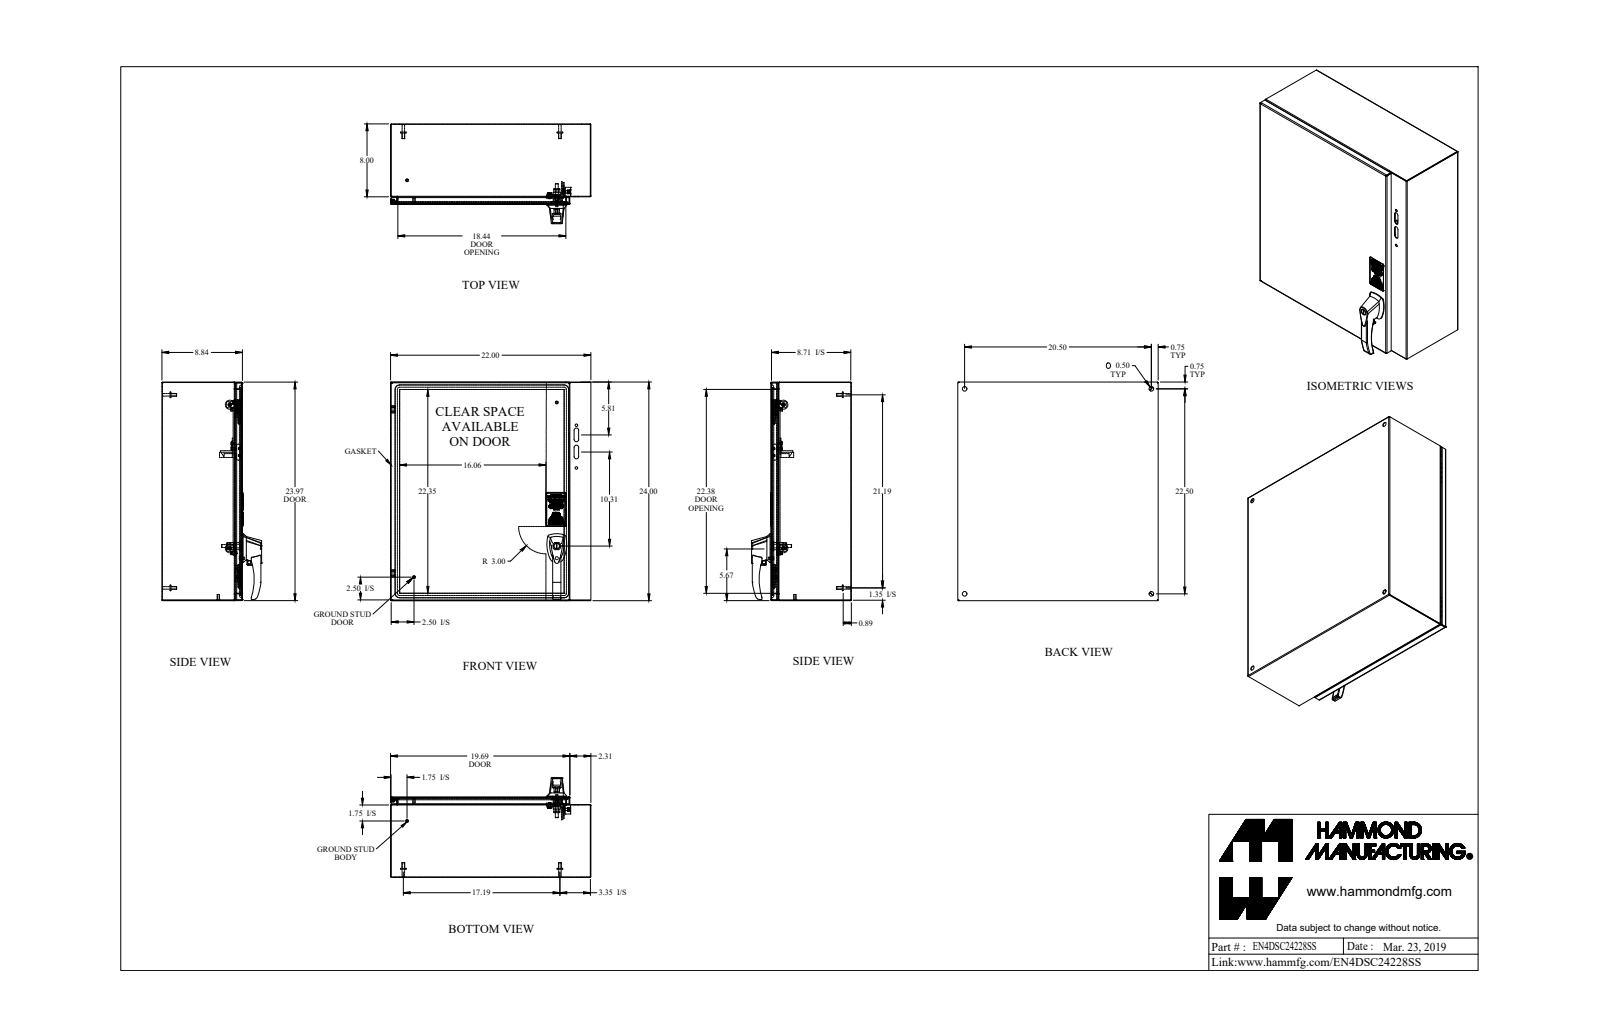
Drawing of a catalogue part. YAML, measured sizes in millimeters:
part_name: "EN4DSC24228GY"
step_written_by: "SolidWorks 2019 (AUTOMOTIVE_DESIGN)"
units: millimeters
bodies: {solids: 44, faces: 922, planar: 498, cylindrical: 283, other: 141}
overall_size: [609.6, 558.8, 278.18]
volume: 2353000
surface_area: 2742000
round_holes:
  - {diameter: 4.47, count: 4}
  - {diameter: 3.97, count: 2}
  - {diameter: 4.39, count: 2}
  - {diameter: 5.46, count: 2}
  - {diameter: 6.35, count: 2}
  - {diameter: 6.73, count: 2}
  - {diameter: 7.14, count: 2}
  - {diameter: 10.49, count: 2}
  - {diameter: 4.37, count: 1}
  - {diameter: 4.98, count: 1}
  - {diameter: 5.92, count: 1}
  - {diameter: 6.1, count: 1}
round_bosses_or_shafts:
  - {diameter: 6.35, count: 7}
  - {diameter: 9.53, count: 4}
  - {diameter: 7.94, count: 4}
  - {diameter: 6.86, count: 4}
  - {diameter: 3.97, count: 4}
  - {diameter: 25.4, count: 2}
  - {diameter: 15.88, count: 2}
  - {diameter: 15.87, count: 2}
partial_cylinders:
  - {radius: 2, count: 28}
  - {radius: 0.55, count: 16}
  - {radius: 6.35, count: 14}
  - {radius: 3.17, count: 11}
  - {radius: 3.45, count: 8}
  - {radius: 0.76, count: 6}
  - {radius: 1.52, count: 6}
  - {radius: 2.29, count: 6}
face_to_face_distances: [1.45, 1.83, 221.18, 222.63, 223.01, 224.46, 557.35, 608.15, 201.75, 558.8]
hole_center_spacings: [400.05, 28.2, 13.21, 19.05, 20.75, 25.2, 25.51, 28.93]
